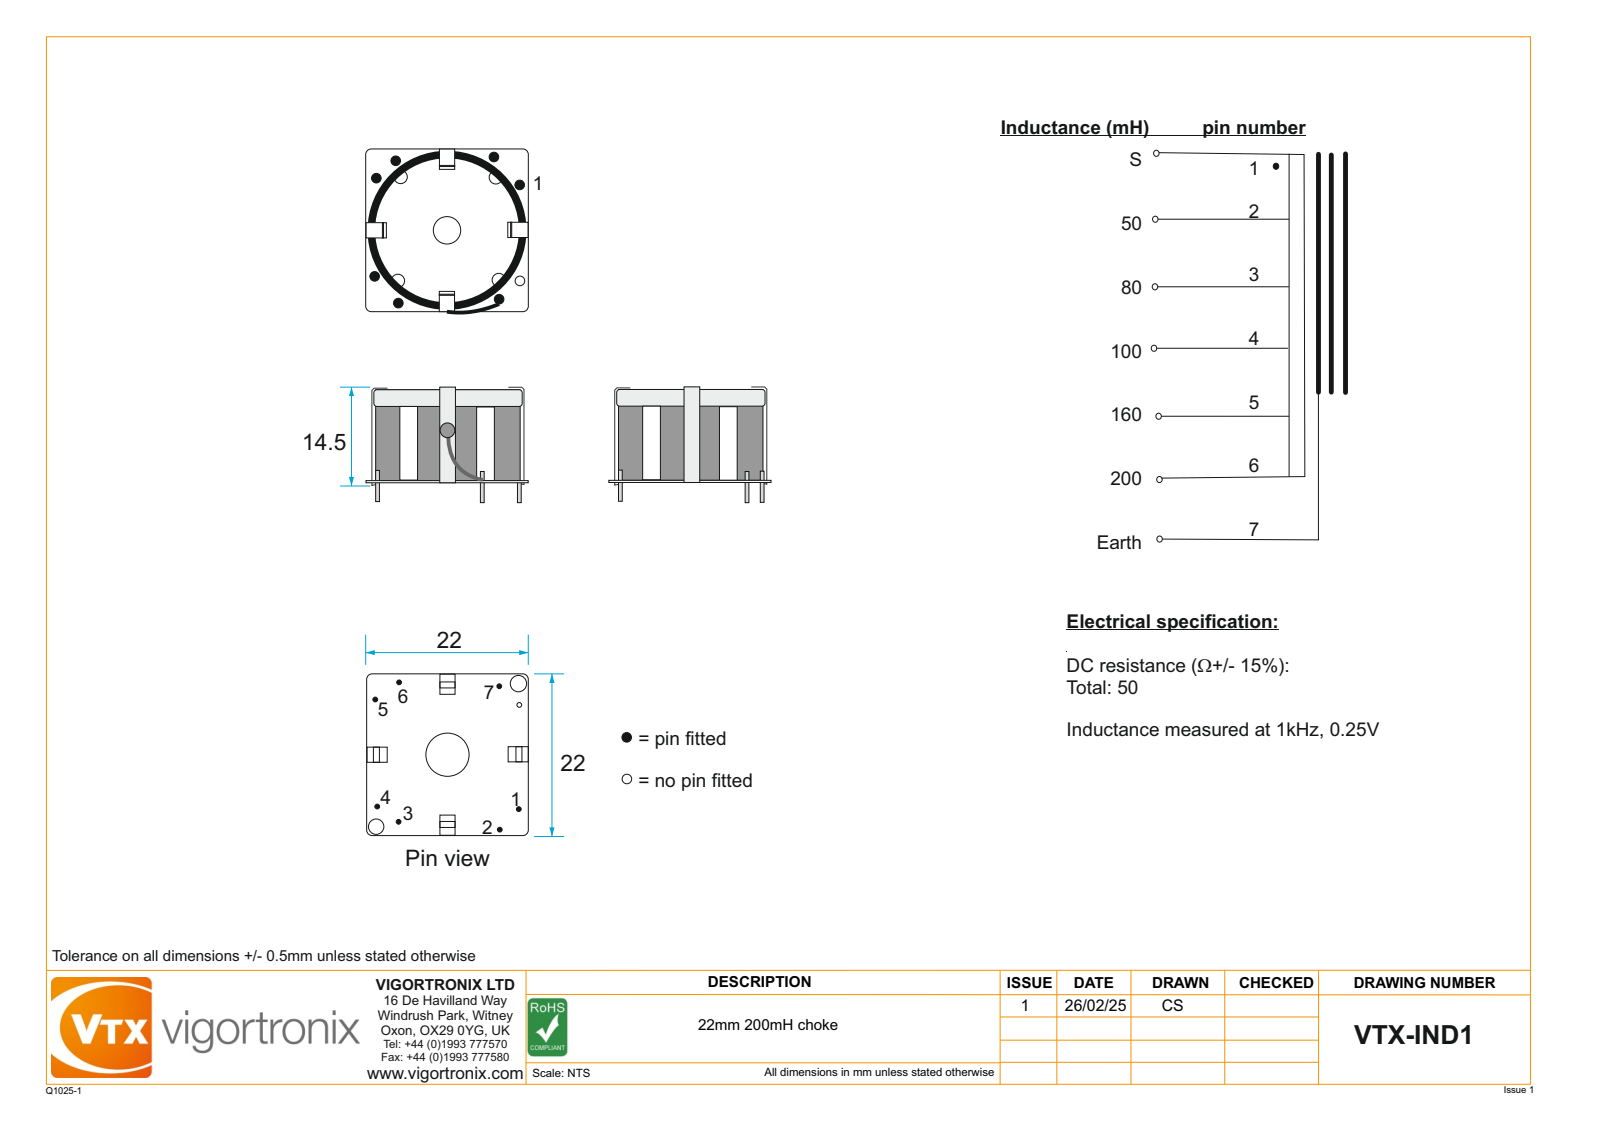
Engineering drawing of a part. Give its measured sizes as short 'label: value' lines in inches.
name: VTX-IND1 Wire YELLOW; VTX-IND1 Top Lid; VTX-IND1 Top Core; VTX-IND1 Wire Grey (+8 more)
written by: SolidWorks 2024 (AUTOMOTIVE_DESIGN)
unit: in
bodies: 43 solids, 679 faces (205 planar, 299 cylindrical, 175 other)
size: 0.866 × 0.866 × 0.738
volume: 0.159 in³; area: 10.23 in²
holes: 8× ⌀0.039, 2× ⌀0.079, 1× ⌀0.098, 1× ⌀0.181, 1× ⌀0.325, 1× ⌀0.354, 1× ⌀0.614, 1× ⌀0.732
bosses: 1× ⌀0.787, 1× ⌀0.35, 1× ⌀0.309
rounds: 48× R0.004, 36× R0.01, 8× R0.02, 8× R0.039, 8× R0.053, 4× R0.006, 4× R0.024, 4× R0.033
face distances: 0.071, 0.441, 0.22, 0.512, 0.37, 0.15, 0.016, 0.142, 0.13, 0.264
hole spacings: 0.43, 0.608, 0.141, 0.5, 0.7, 0.848, 0.86, 0.13
